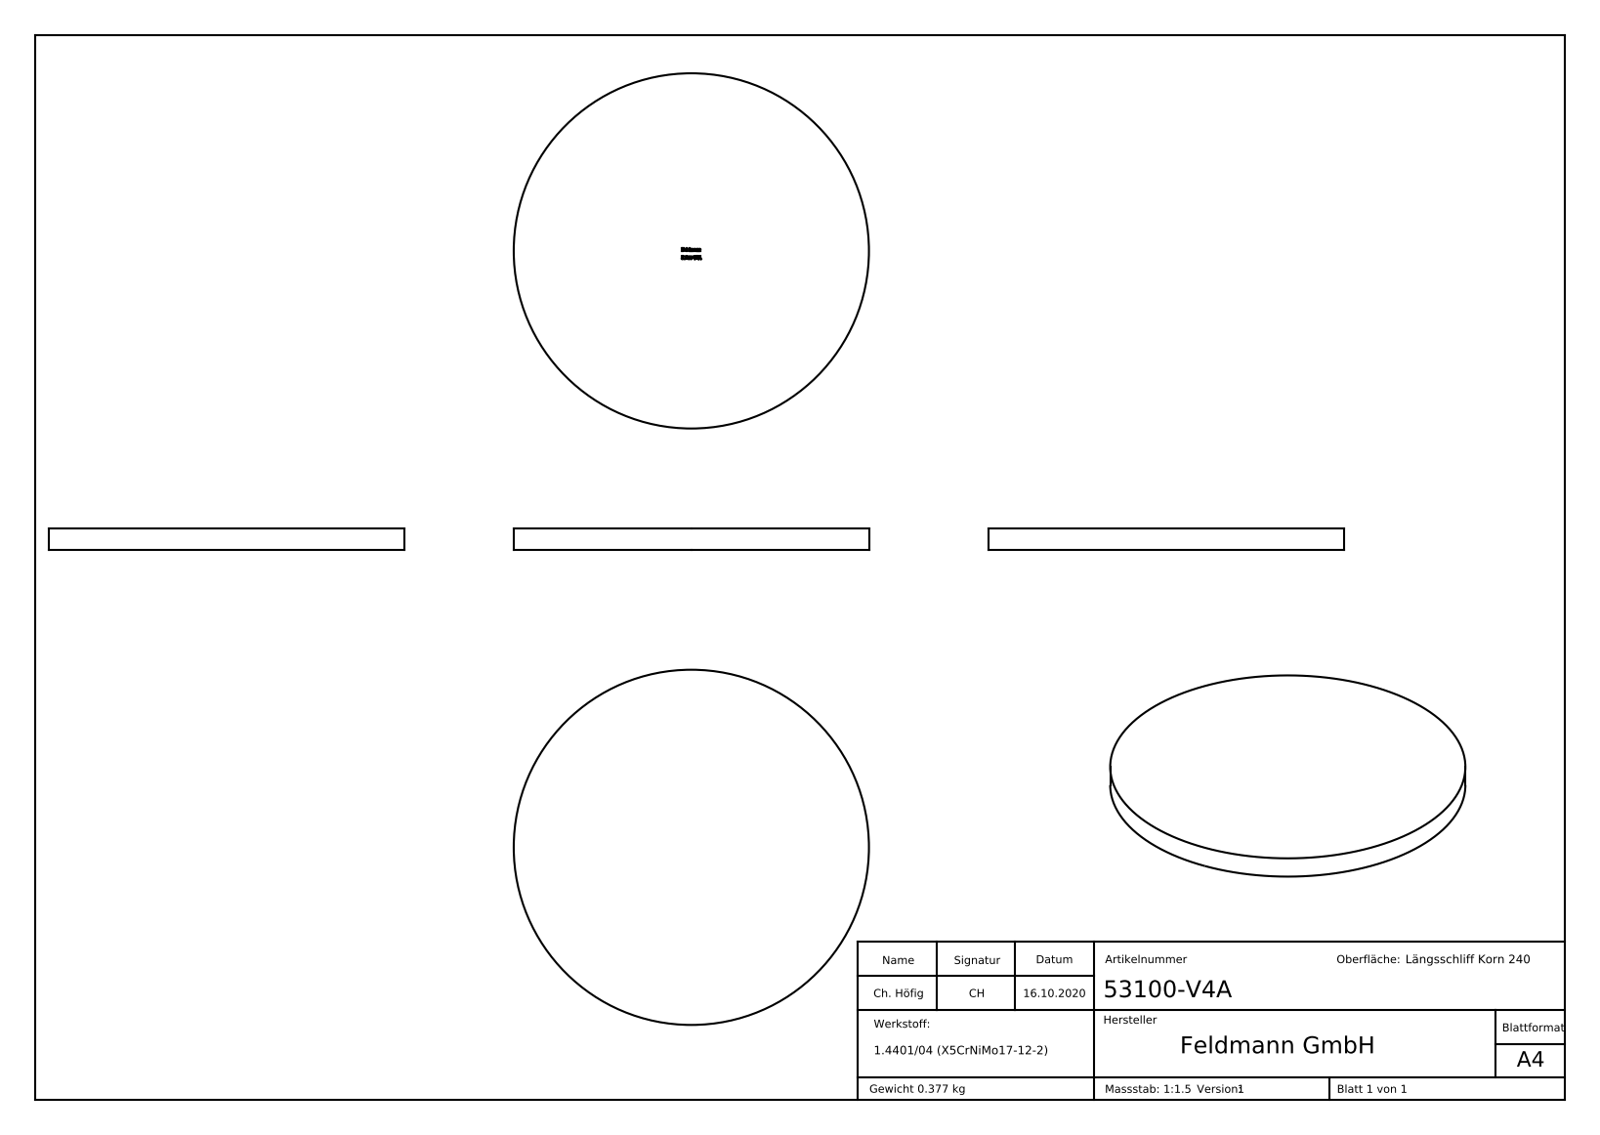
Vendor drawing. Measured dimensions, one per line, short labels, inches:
name: 53100-V4A
written by: SolidWorks 2018 (CONFIG_CONTROL_DESIGN)
unit: in
bodies: 1 solid, 220 faces (130 planar, 2 cylindrical, 88 other)
size: 3.937 × 3.937 × 0.236
volume: 2.876 in³; area: 27.28 in²
bosses: 1× ⌀3.937
face distances: 0.236, 0.232, 0.07, 0.031, 0.096, 0.033, 0.017, 0.039, 0.021, 0.109
